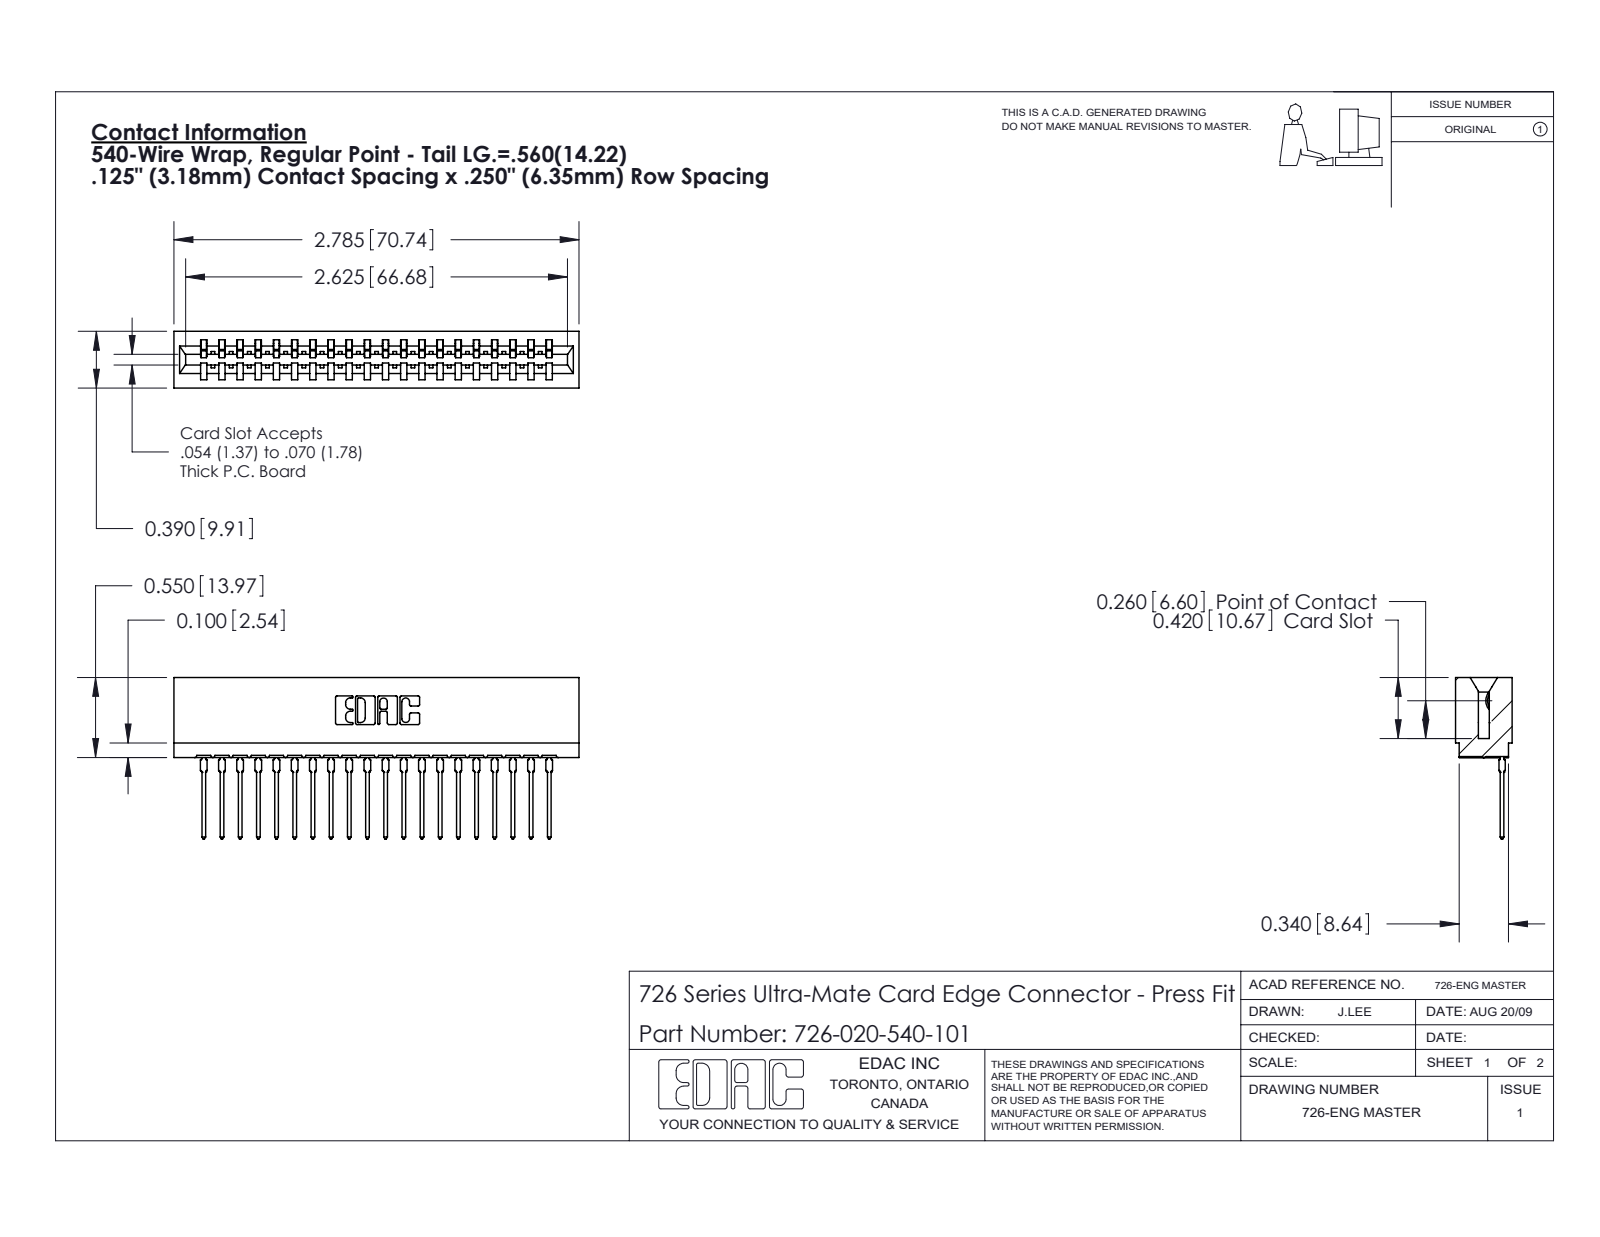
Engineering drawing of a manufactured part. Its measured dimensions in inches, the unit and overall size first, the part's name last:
Units: inches
Overall size (bounding box): 2.785 × 1.109 × 0.39
Partial cylindrical surfaces — rounded edges, fillets, slot ends (radius × count): R0.021 ×40, R0.01 ×22, R0.015 ×21, R0.007 ×6, R0.031 ×6, R0.005 ×4, R0.011 ×4, R0.026 ×3
Main face-to-face distances: 0.057, 0.333, 0.25, 0.39, 0.025, 0.307, 0.5, 0.75, 0.083, 0.375
Volume: 0.396 in³ · Surface area: 15.22 in²
Bodies: 21 solids, 2257 faces (1315 planar, 422 cylindrical, 520 other)
Part name (STEP PRODUCT): 726 Part_.515 Slot Depth - 01; 746-292-001_540; 726-020-540-101
STEP written by: SolidWorks 2020 (CONFIG_CONTROL_DESIGN)
